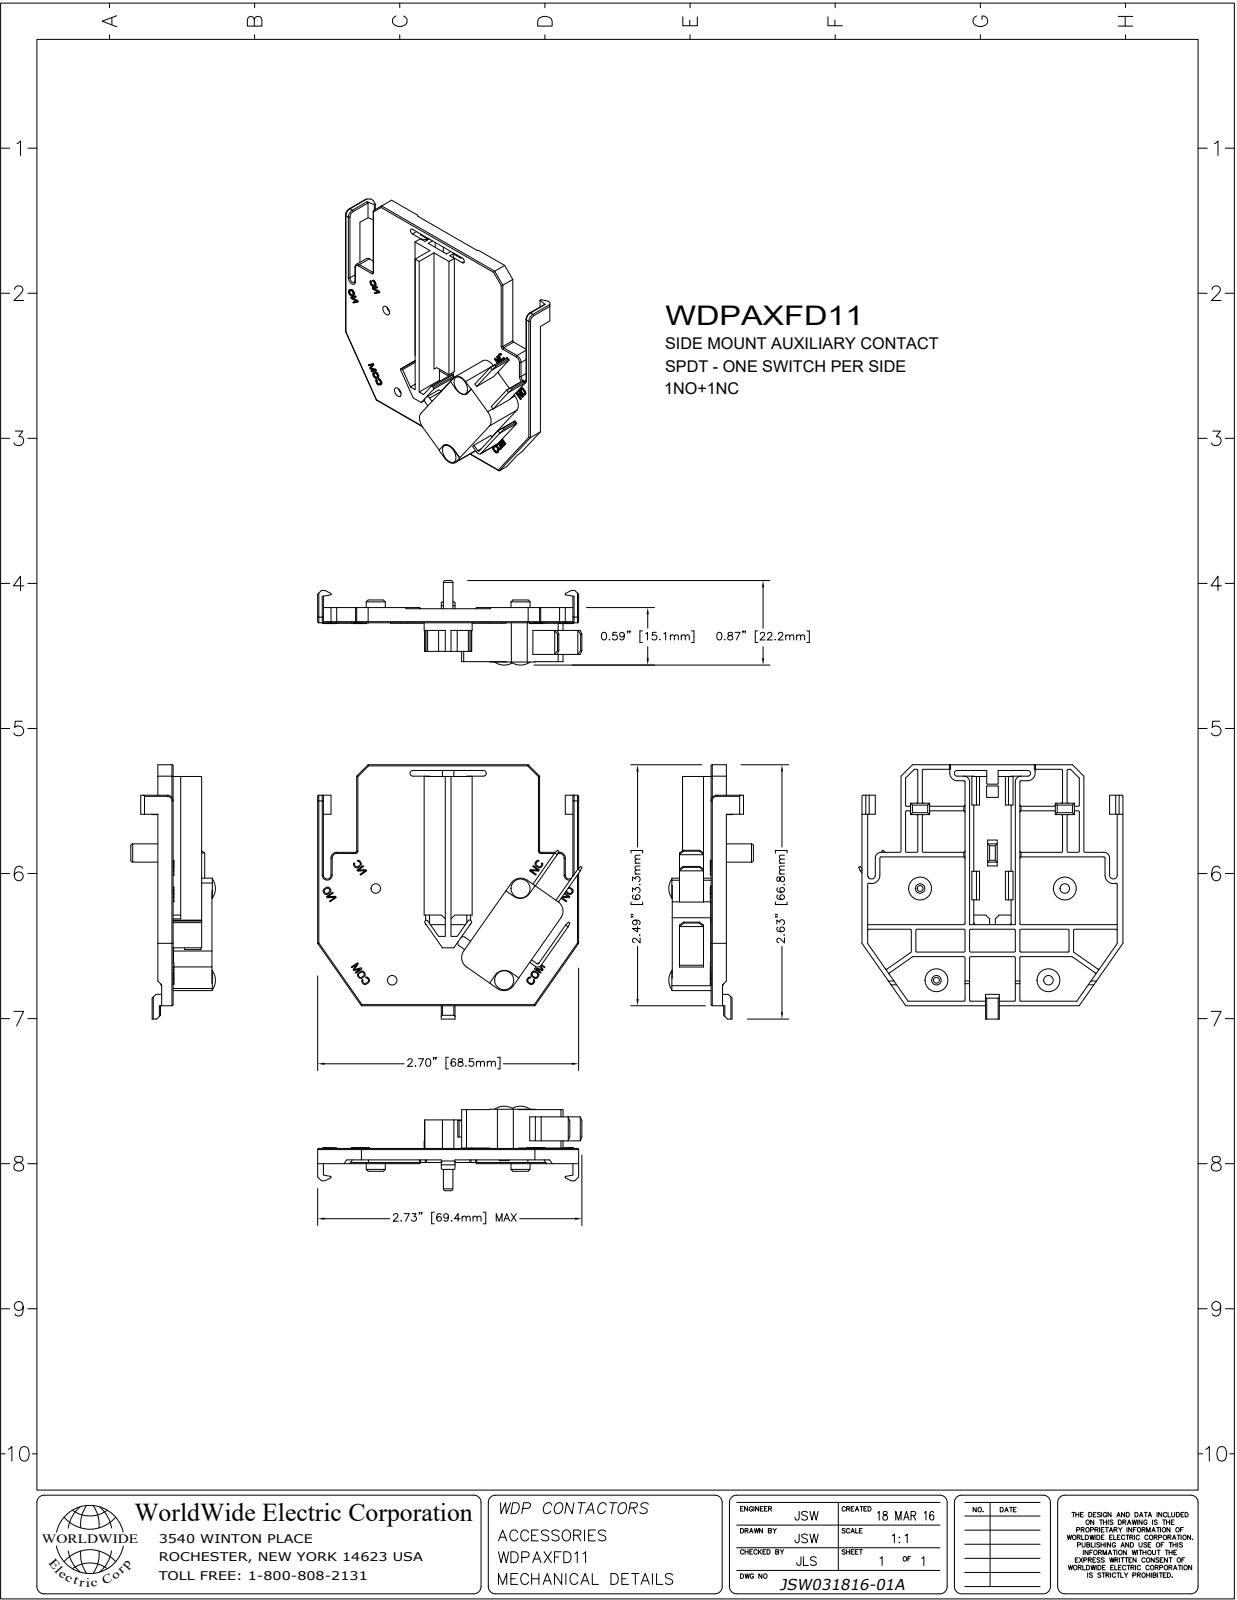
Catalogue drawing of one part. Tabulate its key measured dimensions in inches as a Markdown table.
| quantity | value |
| --- | --- |
| part name | WDPAXFD11 |
| STEP written by | SolidWorks 2021 (CONFIG_CONTROL_DESIGN) |
| units | inches |
| bodies | 5 solids, 936 faces (745 planar, 171 cylindrical, 20 other) |
| overall size | 2.73 × 2.63 × 0.874 |
| volume | 0.768 in³ |
| surface area | 24.34 in² |
| round holes (diameter × count) | 0.098 × 4, 0.06 × 2, 0.122 × 2 |
| round bosses / shafts (diameter × count) | 0.236 × 4 |
| partial cylindrical surfaces (radius × count) | 0.012 × 103, 0.039 × 6, 0.118 × 6, 0.059 × 5, 0.008 × 4, 0.02 × 4, 0.03 × 2, 0.031 × 2 |
| main face-to-face distances | 0.047, 0.059, 0.079, 1.319, 0.098, 0.236, 0.323, 0.126, 0.402, 0.11 |
| hole center spacings | 0.963, 1.631, 1.157, 1.496 |
